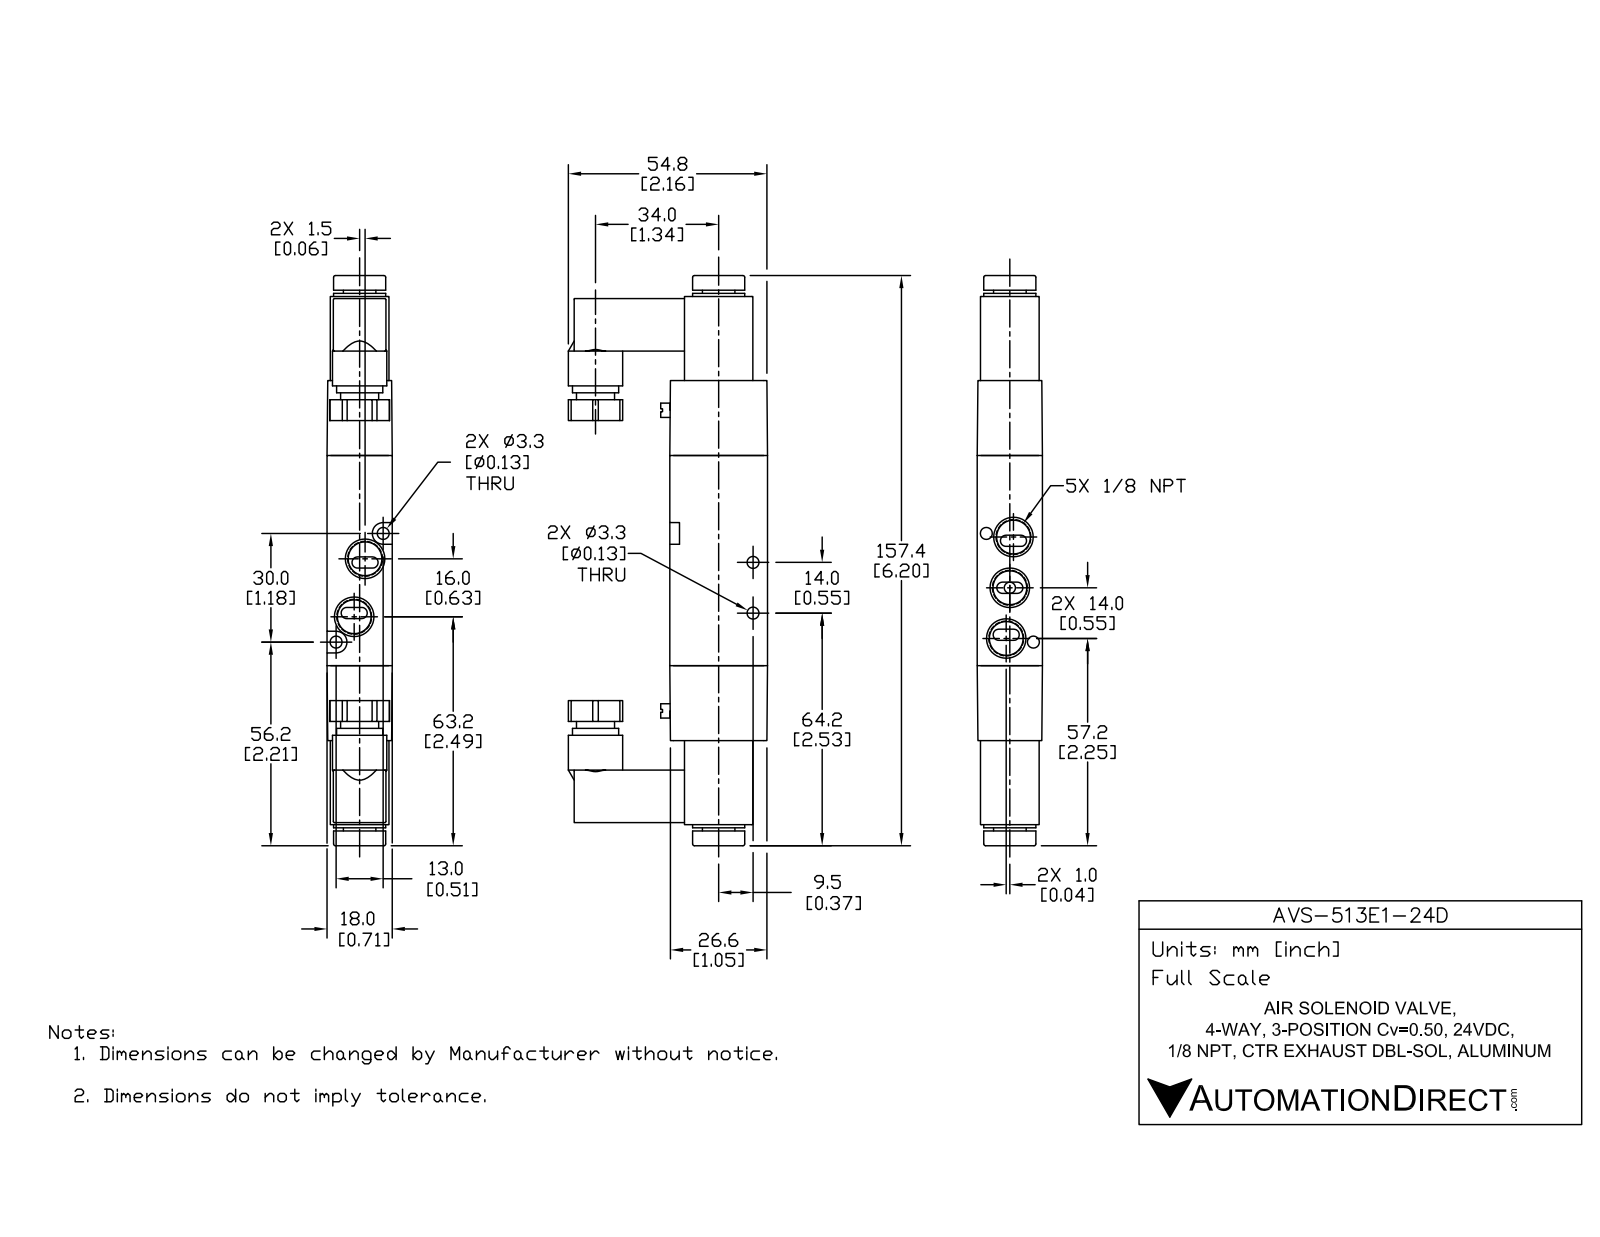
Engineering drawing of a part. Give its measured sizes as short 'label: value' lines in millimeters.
name: AVS-513E1-24D
written by: SolidWorks 2021 (CONFIG_CONTROL_DESIGN)
unit: mm
bodies: 5 solids, 246 faces (131 planar, 91 cylindrical, 24 other)
size: 157.4 × 55 × 18
volume: 77 332 mm³; area: 24 997 mm²
holes: 5× ⌀8.43, 2× ⌀3.2, 2× ⌀3.3, 1× ⌀9.3
bosses: 2× ⌀6.8, 1× ⌀15, 1× ⌀14.4, 1× ⌀12.8, 1× ⌀10.5, 1× ⌀9
rounds: 10× R1.54, 8× R0.3, 8× R0.5, 8× R1, 2× R3
face distances: 1.75, 16.25, 18.21, 0.31, 14.5, 18, 23.66, 18.52, 58, 3.86
hole spacings: 7.57, 14.04, 16.35, 29.52, 6.25, 6.82, 8.04, 8.19
